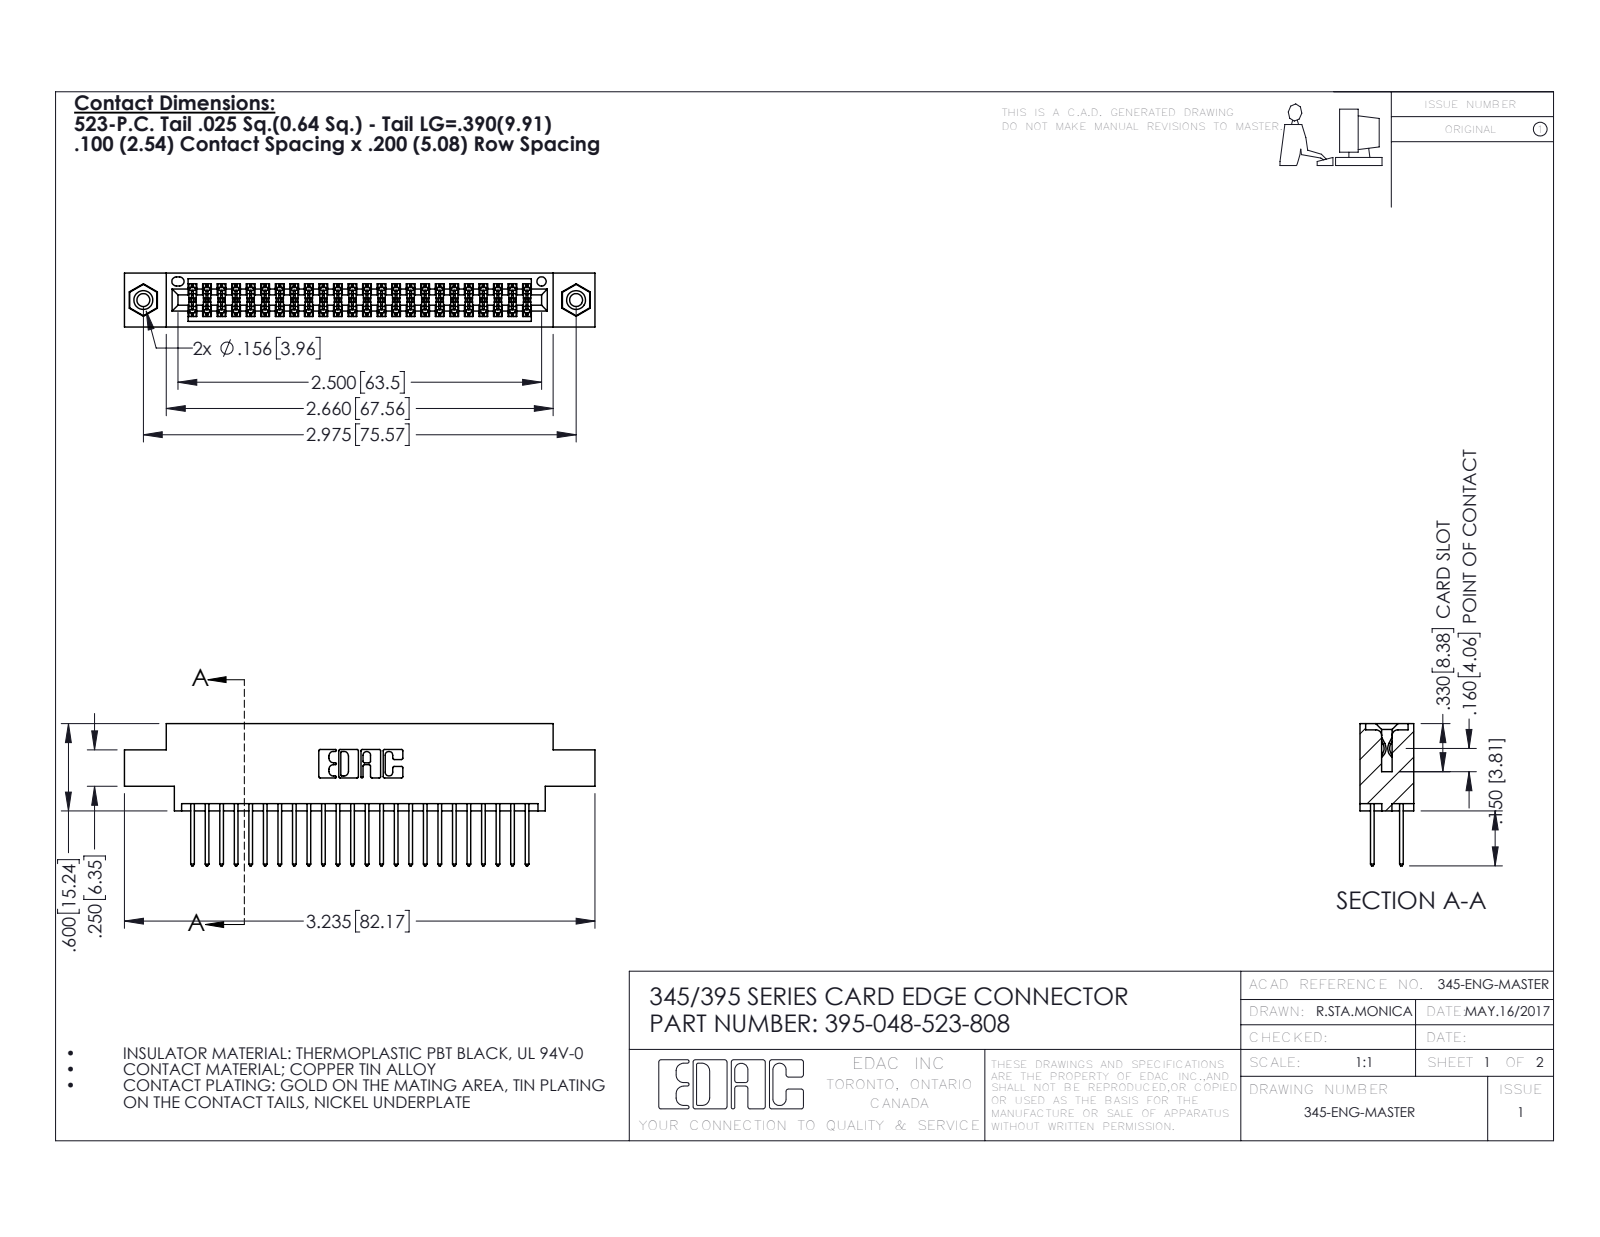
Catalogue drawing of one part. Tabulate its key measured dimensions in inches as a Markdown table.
| quantity | value |
| --- | --- |
| part name | 345-250-001_345-250-003-102; 345-292-001_345-293-123; 345 Part_0.170 Offset - 0.156 Dia-TI; 395-048-523-808 |
| STEP written by | SolidWorks 2016 (CONFIG_CONTROL_DESIGN) |
| units | inches |
| bodies | 51 solids, 2590 faces (1700 planar, 874 cylindrical, 16 other) |
| overall size | 3.235 × 0.977 × 0.37 |
| volume | 0.476 in³ |
| surface area | 18.24 in² |
| round holes (diameter × count) | 0.089 × 2, 0.125 × 2, 0.156 × 2, 0.064 × 1 |
| round bosses / shafts (diameter × count) | 0.155 × 2 |
| partial cylindrical surfaces (radius × count) | 0.006 × 72, 0.01 × 48, 0.01 × 22, 0.007 × 6, 0.031 × 6, 0.026 × 3, 0.014 × 2, 0.019 × 2 |
| main face-to-face distances | 0.072, 0.298, 0.2, 0.098, 0.272, 0.025, 0.37, 0.225, 0.175, 0.149 |
| hole center spacings | 0.27, 2.741, 2.975 |
